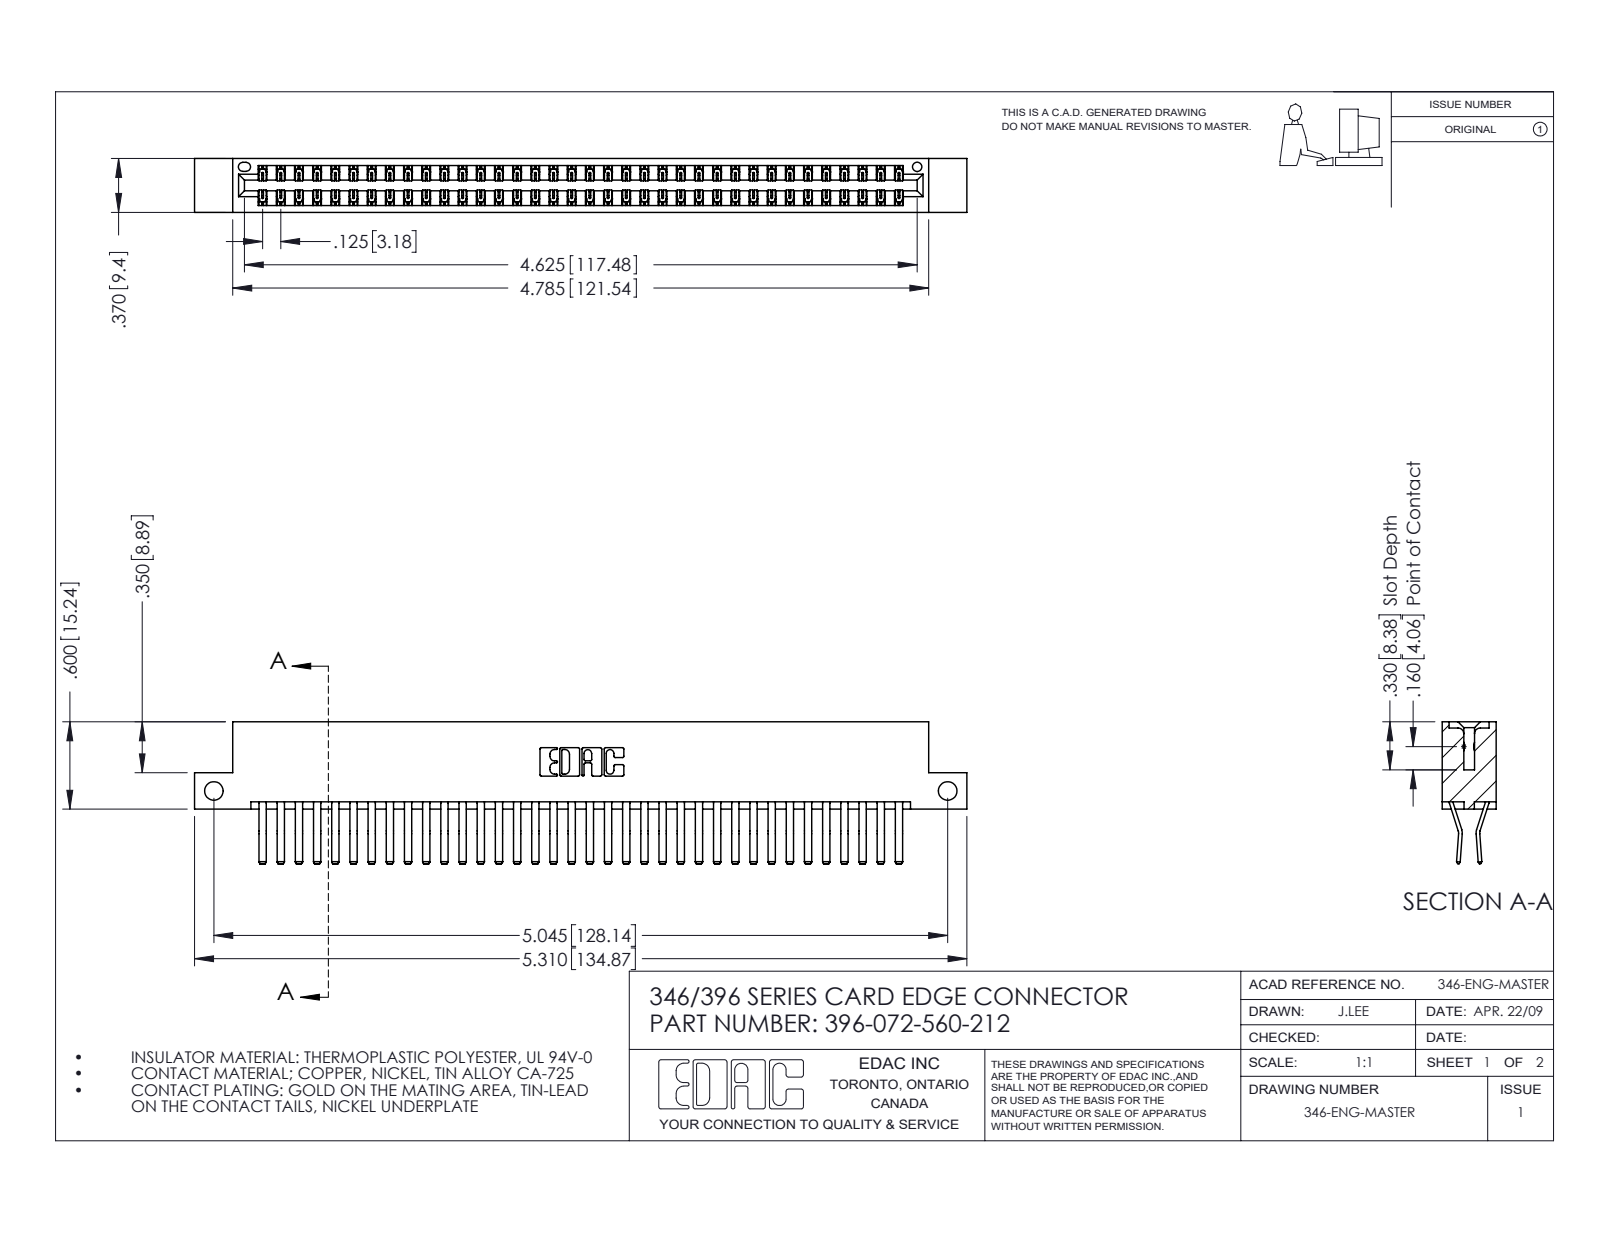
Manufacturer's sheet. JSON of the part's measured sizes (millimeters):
{"part_name": "396-072-560-212; 345-292-001_560 Tail; 346 Part_Flush Mounting Lugs - Side Mount", "step_written_by": "SolidWorks 2016 (CONFIG_CONTROL_DESIGN)", "units": "millimeters", "bodies": {"solids": 73, "faces": 4010, "planar": 2596, "cylindrical": 1414, "other": 0}, "overall_size": [134.9, 24.8, 9.4], "volume_mm3": 13500, "surface_area_mm2": 19570, "round_holes": [[3.3, 2], [1.6, 1]], "partial_cylinders_radius": [[0.2, 108], [0.3, 22], [0.2, 6], [0.8, 6], [0.7, 3], [0.3, 2], [0.4, 2], [0.6, 2]], "face_to_face_distances": [1.2, 8.2, 9.4, 0.6, 6.4, 1.8, 7.6, 7, 3.8, 5.6], "hole_center_spacings": [128.1]}
